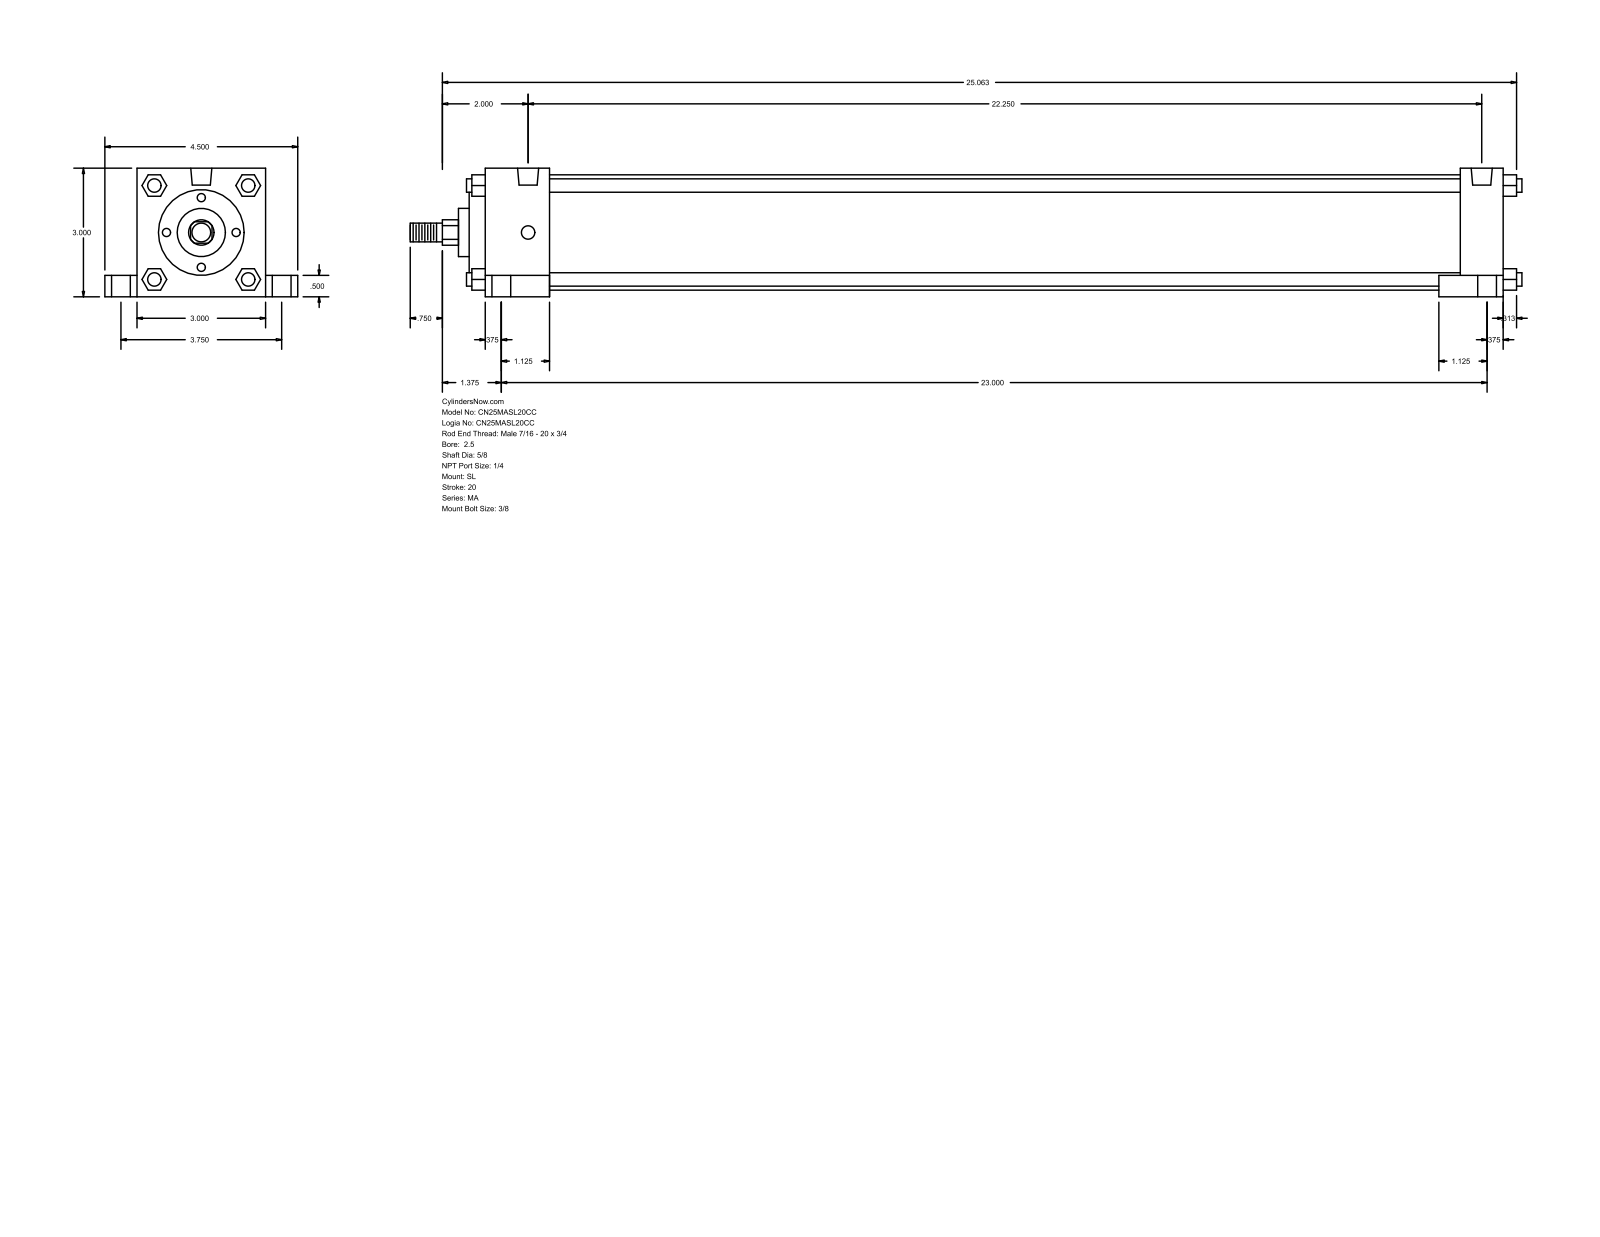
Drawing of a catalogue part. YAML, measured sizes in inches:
part_name: "MA_SL__0250_0.625"
step_written_by: "GSSL Pune (CONFIG_CONTROL_DESIGN)"
units: inches
bodies: {solids: 0, faces: 150, planar: 113, cylindrical: 37, other: 0}
overall_size: [25.937, 4.5, 3]
round_holes:
  - {diameter: 0.313, count: 4}
  - {diameter: 0.437, count: 4}
  - {diameter: 0.687, count: 4}
  - {diameter: 0.492, count: 2}
round_bosses_or_shafts:
  - {diameter: 0.313, count: 4}
  - {diameter: 2.69, count: 1}
  - {diameter: 2, count: 1}
  - {diameter: 1.125, count: 1}
  - {diameter: 0.625, count: 1}
  - {diameter: 0.437, count: 1}
partial_cylinders:
  - {radius: 0.297, count: 1}
face_to_face_distances: [3, 23.75, 0.5, 21.25, 1, 1.5, 22.25, 22.75, 0.75, 2.5]
hole_center_spacings: [1.879, 1.976, 3.75, 22.25, 22.453, 22.952, 23, 23.304]
